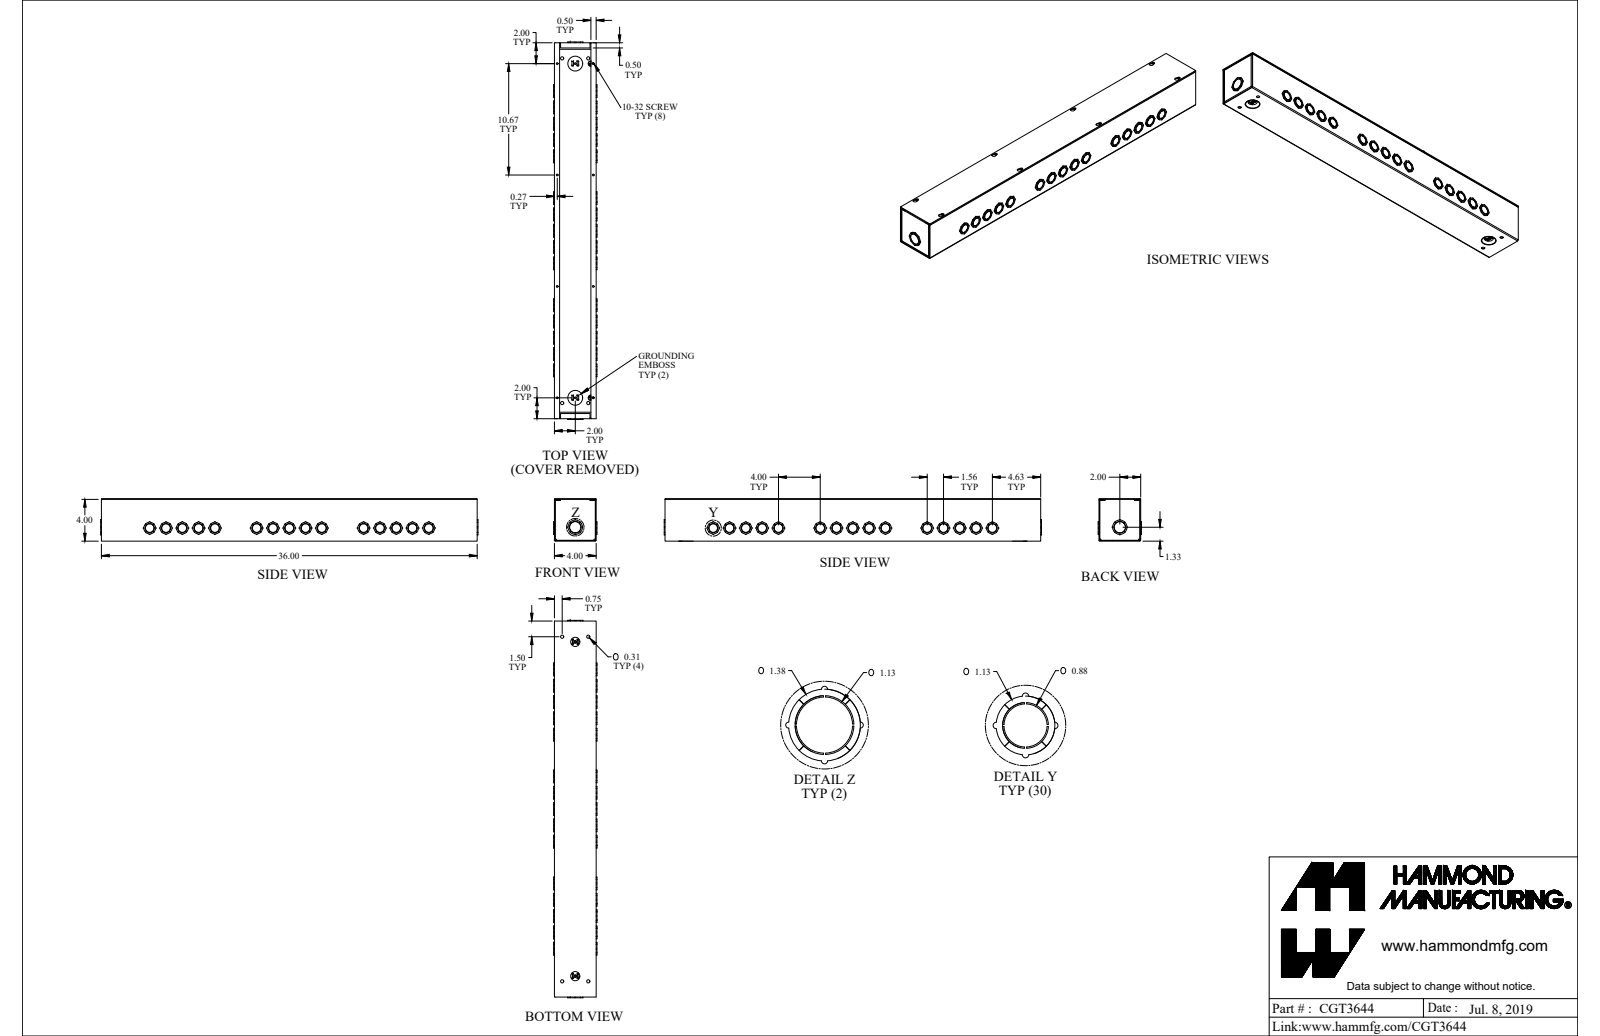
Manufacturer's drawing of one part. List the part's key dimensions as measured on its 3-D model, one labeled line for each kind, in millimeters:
Part name (STEP PRODUCT): CGT3644
STEP written by: SolidWorks 2021 (AUTOMOTIVE_DESIGN)
Units: millimetres
Bodies: 6 solids, 1618 faces (756 planar, 848 cylindrical, 14 other)
Overall size (bounding box): 918.1 × 107.9 × 105.3
Volume: 684 200 mm³ · Surface area: 855 500 mm²
Round holes (diameter × count): ⌀22.2 ×15, ⌀4.3 ×10, ⌀7.9 ×4, ⌀12.7 ×2, ⌀28.6 ×1
Round bosses / shafts (diameter × count): ⌀28.6 ×15, ⌀21 ×15, ⌀12.5 ×2, ⌀9.5 ×2, ⌀7.2 ×2, ⌀4.8 ×2, ⌀34.9 ×1, ⌀27.3 ×1
Partial cylindrical surfaces — rounded edges, fillets, slot ends (radius × count): R1.6 ×60, R0.9 ×8, R1.4 ×8, R2.7 ×8, R3.2 ×8, R5.2 ×8, R0.7 ×4, R1.4 ×4
Main face-to-face distances: 1.4, 100.2, 101.6, 1.8, 98.7, 103.4, 102, 3.3, 912.6, 914.4
Hole centre spacings: 79.3, 260.3, 39.7, 39.7, 180.9, 220.6, 300, 17.6
